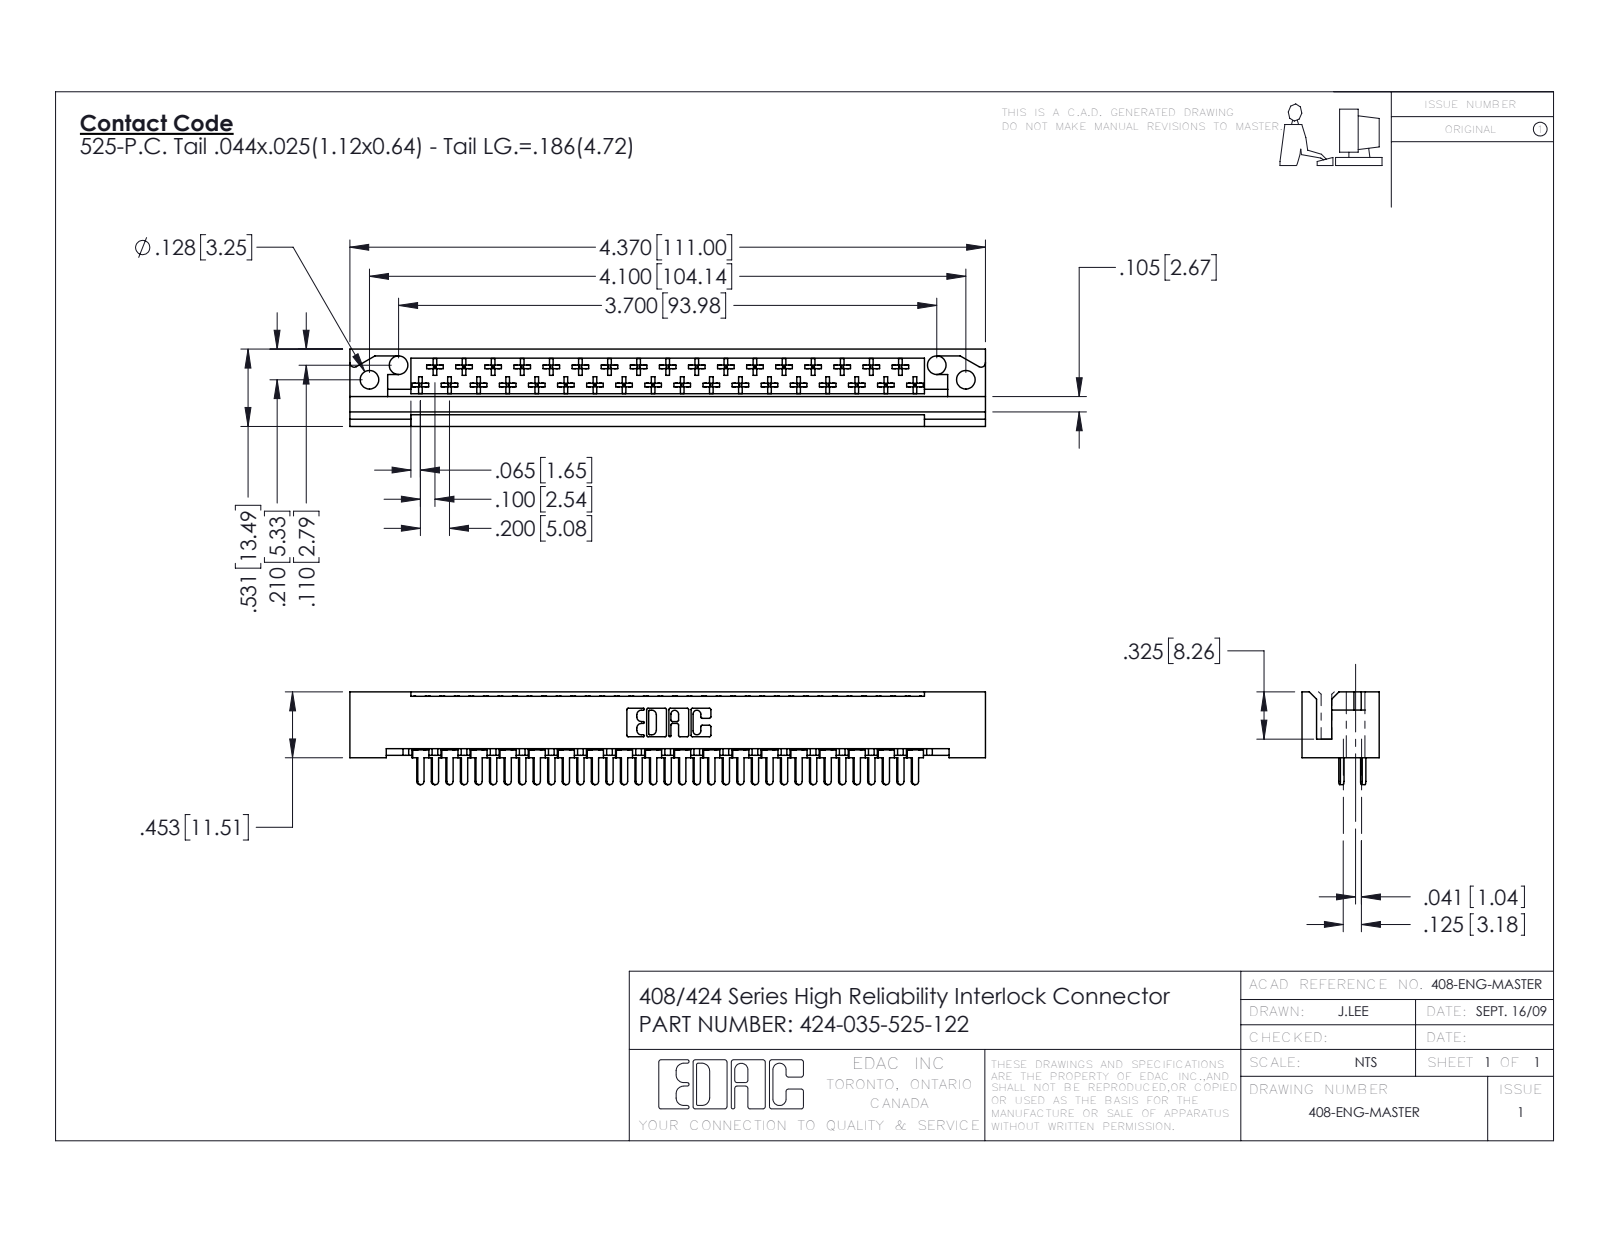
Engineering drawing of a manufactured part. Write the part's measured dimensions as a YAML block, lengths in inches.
part_name: "424 Part_035; 408-290-001_408-290-125 - Top; 424-035-525-122; 408-290-001_408-290-125 - Bottom"
step_written_by: "SolidWorks 2016 (CONFIG_CONTROL_DESIGN)"
units: inches
bodies: {solids: 36, faces: 2070, planar: 1559, cylindrical: 371, other: 140}
overall_size: [4.37, 0.638, 0.531]
volume: 0.701
surface_area: 23.42
round_holes:
  - {diameter: 0.128, count: 4}
partial_cylinders:
  - {radius: 0.01, count: 210}
  - {radius: 0.02, count: 37}
  - {radius: 0.022, count: 35}
  - {radius: 0.01, count: 22}
  - {radius: 0.007, count: 6}
  - {radius: 0.031, count: 6}
  - {radius: 0.026, count: 3}
  - {radius: 0.03, count: 2}
face_to_face_distances: [0.1, 0.296, 0.025, 0.531, 0.125, 0.217, 0.272, 0.235, 0.259, 0.025]
hole_center_spacings: [0.224, 3.901, 3.7, 4.1]
